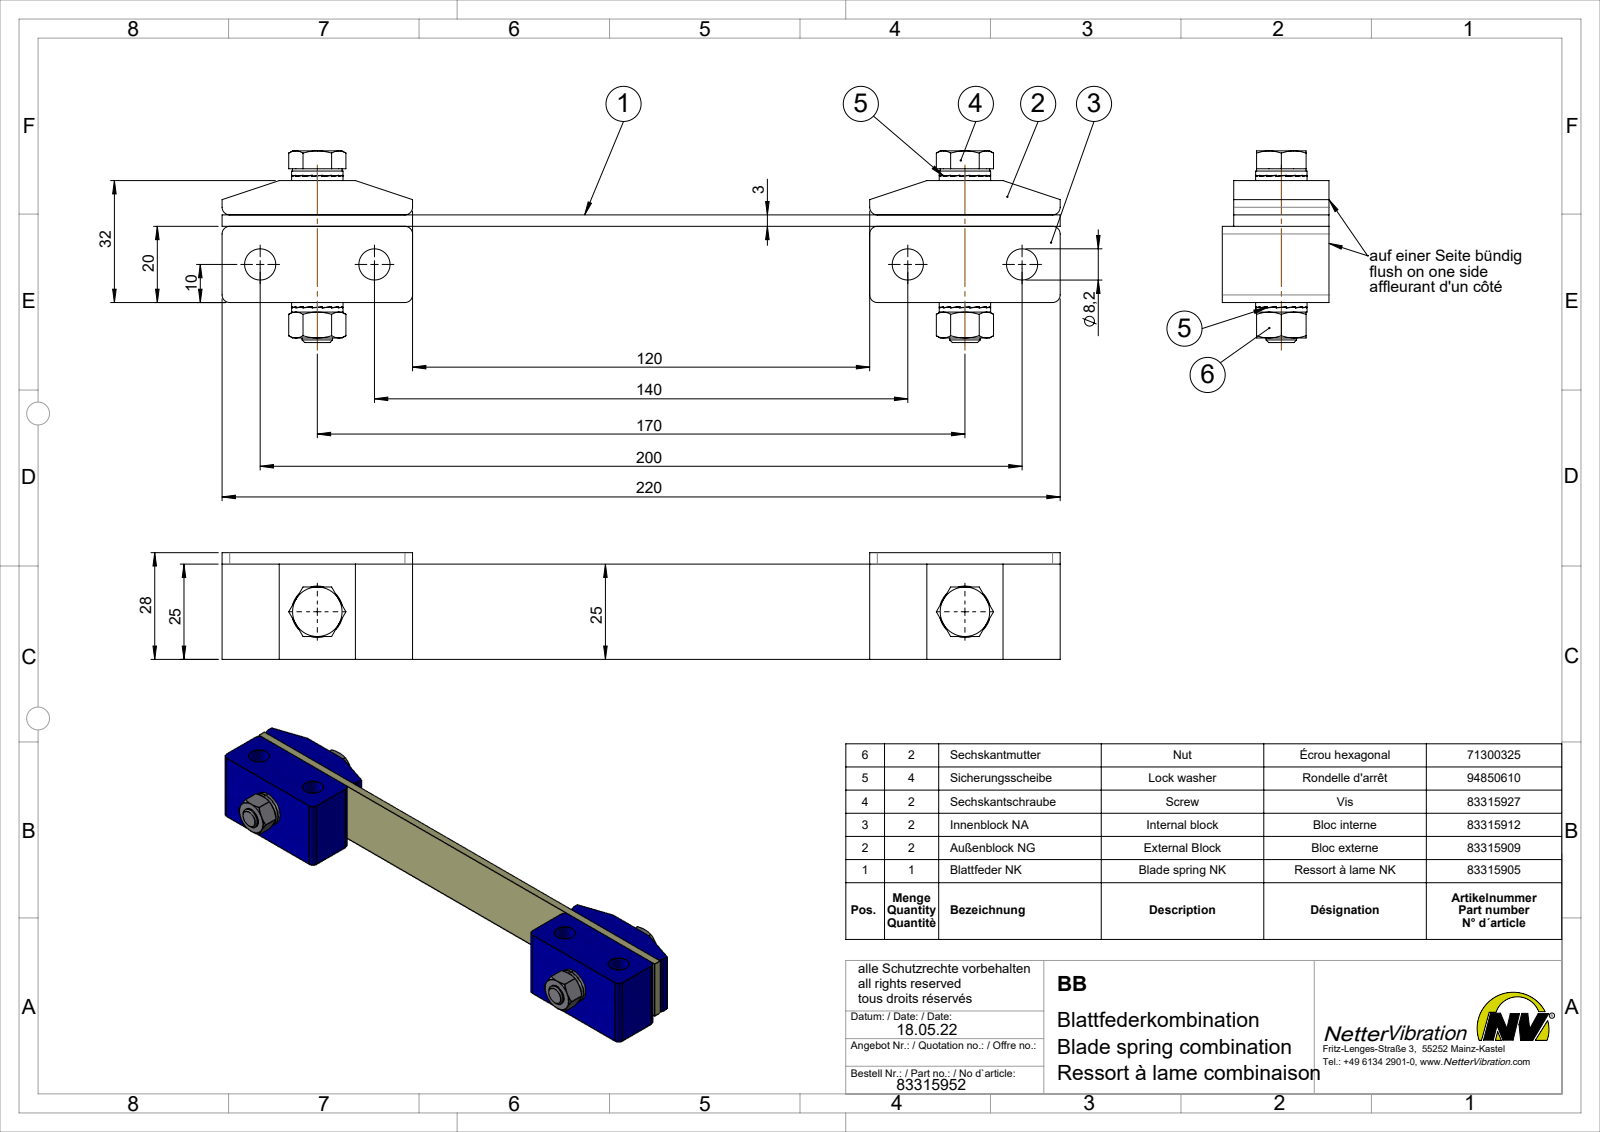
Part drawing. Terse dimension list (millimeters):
name: Blattfederkombination BB # 83315952
written by: SolidWorks 2015 (AUTOMOTIVE_DESIGN)
unit: mm
bodies: 13 solids, 660 faces (536 planar, 72 cylindrical, 52 other)
size: 220 × 50.3 × 28
volume: 90 094 mm³; area: 40 650 mm²
holes: 6× ⌀8.2, 2× ⌀6.8, 2× ⌀8, 2× ⌀8.5, 2× ⌀8.7
bosses: 2× ⌀13.5, 2× ⌀13
rounds: 8× R2, 4× R0.5
face distances: 3, 23, 20, 28, 25, 9, 12, 32, 170, 50
hole spacings: 170, 30, 140, 200
